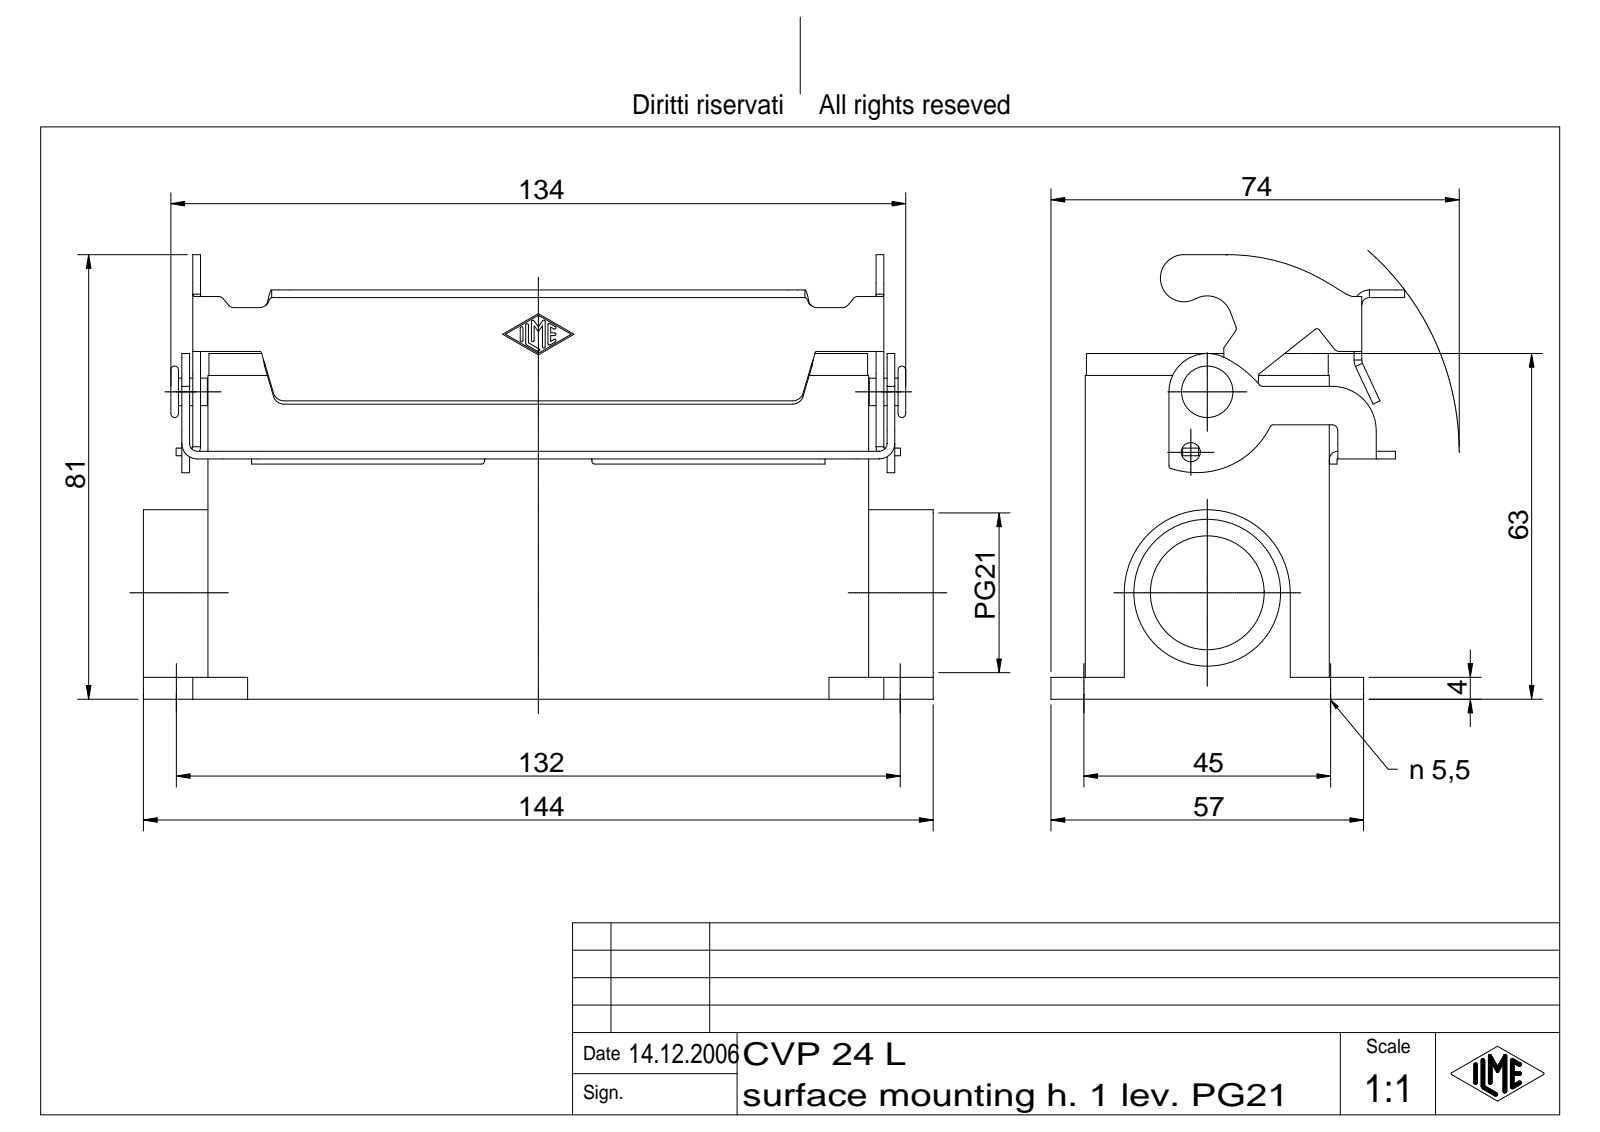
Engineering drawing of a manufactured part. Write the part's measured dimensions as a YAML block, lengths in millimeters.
part_name: "CVP 24 L"
step_written_by: "Autodesk Inventor 7 (AUTOMOTIVE_DESIGN)"
units: millimeters
bodies: {solids: 2, faces: 401, planar: 141, cylindrical: 116, other: 144}
overall_size: [144, 81, 64.48]
volume: 128079
surface_area: 69915
round_holes:
  - {diameter: 5.5, count: 4}
  - {diameter: 3.5, count: 1}
  - {diameter: 20.78, count: 1}
  - {diameter: 26.78, count: 1}
round_bosses_or_shafts:
  - {diameter: 5, count: 1}
  - {diameter: 3.2, count: 1}
  - {diameter: 3, count: 1}
partial_cylinders:
  - {radius: 0.25, count: 15}
  - {radius: 0.5, count: 9}
  - {radius: 1.5, count: 9}
  - {radius: 1, count: 8}
  - {radius: 1.4, count: 6}
  - {radius: 2, count: 6}
  - {radius: 2.8, count: 6}
  - {radius: 1.8, count: 4}
face_to_face_distances: [4, 40.5, 44.5, 36.5, 11.75, 1.4, 40.3, 120.5, 108.75, 15.75]
hole_center_spacings: [45, 132, 139.46, 25.79]
